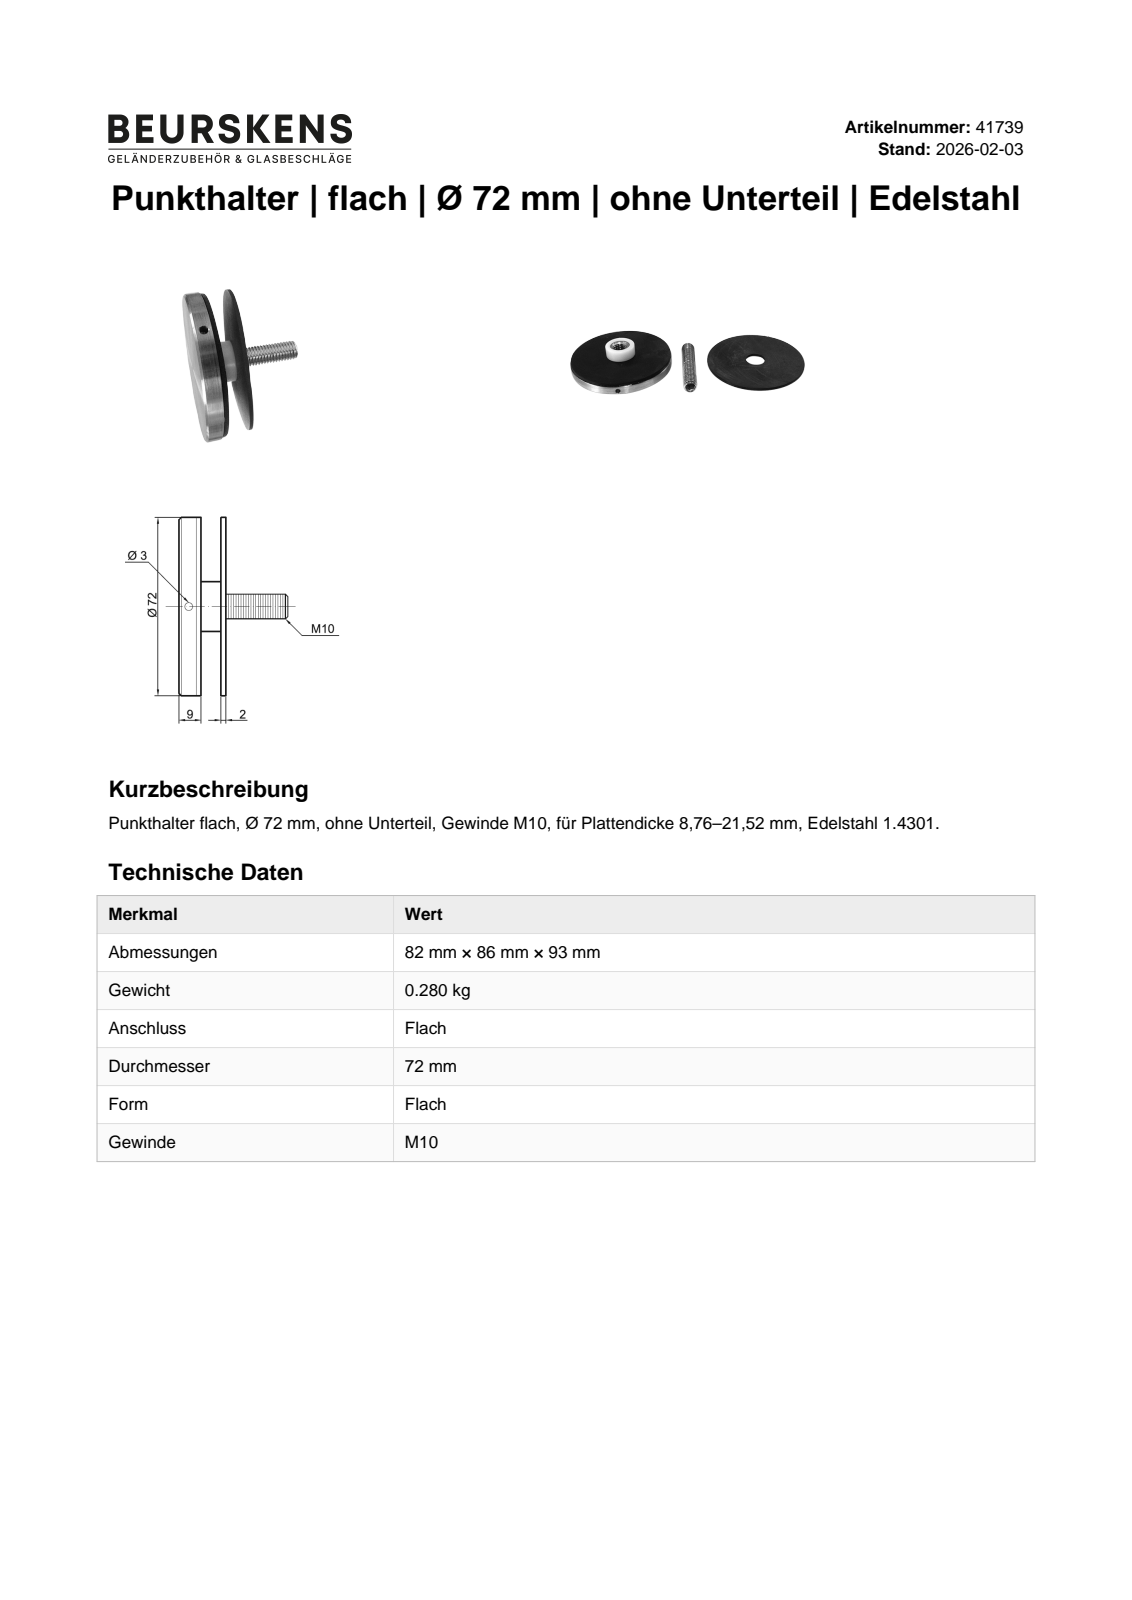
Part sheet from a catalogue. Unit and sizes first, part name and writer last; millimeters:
Units: millimetres
Overall size (bounding box): 72 × 72 × 67
Round holes (diameter × count): ⌀3 ×1, ⌀10 ×1, ⌀14 ×1, ⌀14.2 ×1
Round bosses / shafts (diameter × count): ⌀72 ×1, ⌀70 ×1, ⌀20.2 ×1
Main face-to-face distances: 10, 2, 7, 17, 8, 9, 12, 19, 5.19, 50
Volume: 49 712 mm³ · Surface area: 29 573 mm²
Bodies: 5 solids, 41 faces (25 planar, 11 cylindrical, 5 other)
Part name (STEP PRODUCT): 41739; Kopf 41739; 40903; 40910 Kunststoff weiß (+1 more)
STEP written by: Autodesk Inventor 2023 (AUTOMOTIVE_DESIGN)
